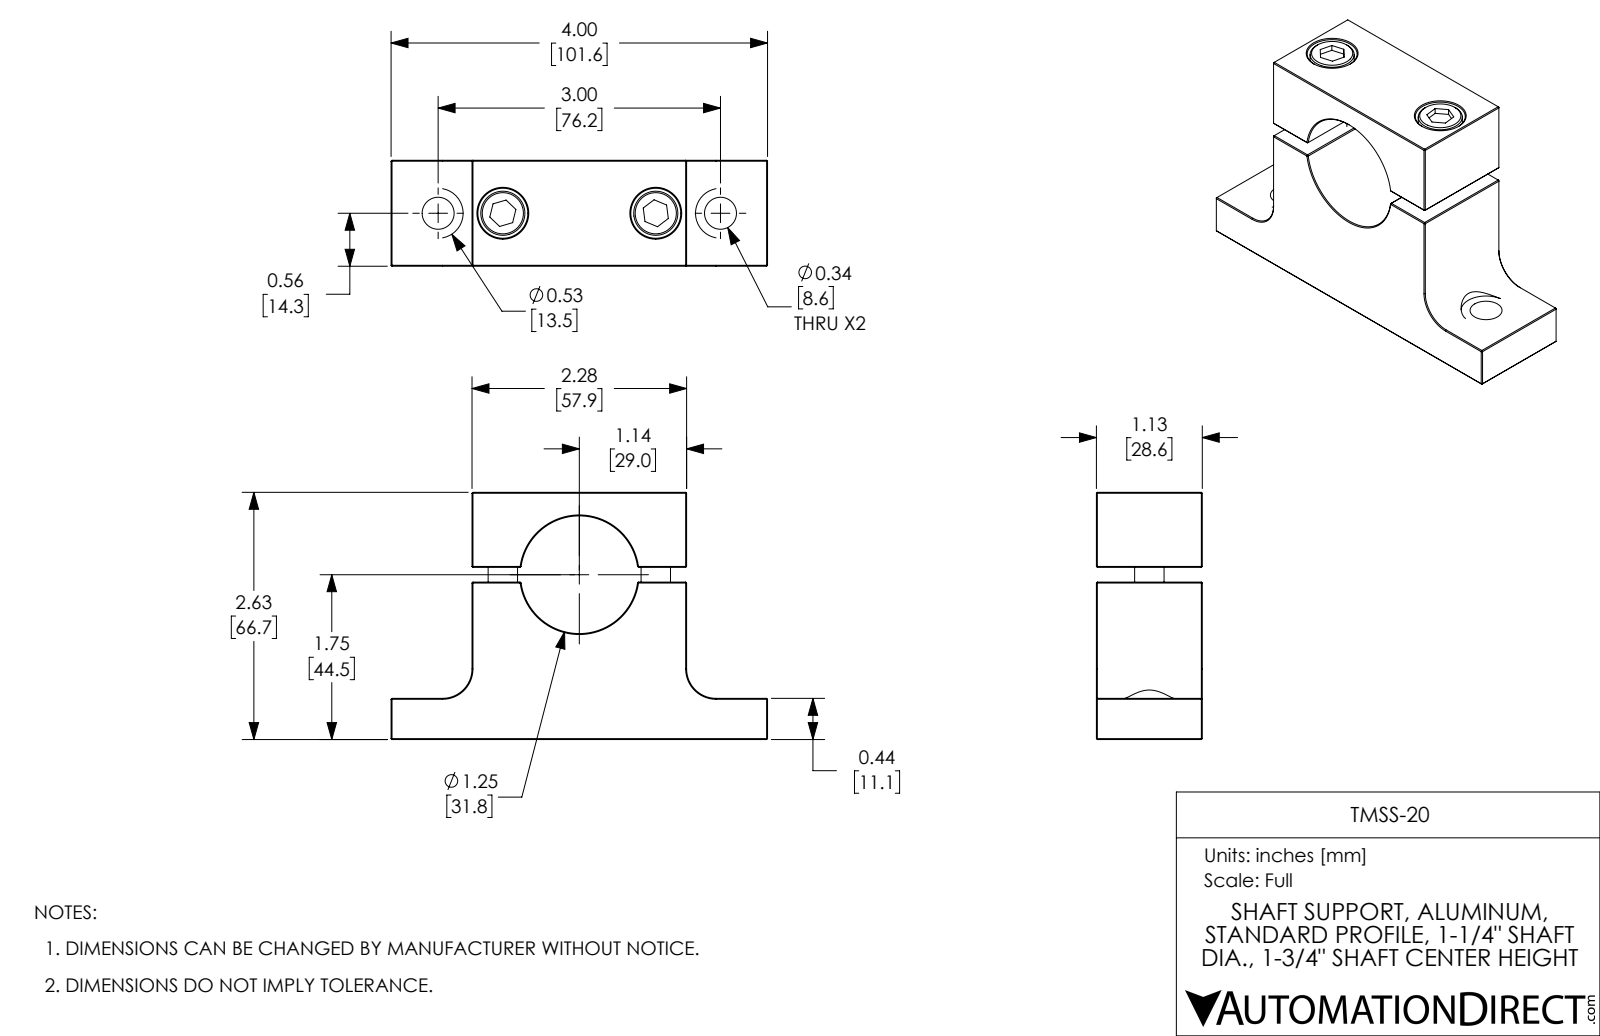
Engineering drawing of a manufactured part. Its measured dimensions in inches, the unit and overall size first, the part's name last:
Units: inches
Overall size (bounding box): 4 × 2.625 × 1.125
Round holes (diameter × count): ⌀0.252 ×2, ⌀0.332 ×2, ⌀0.34 ×2, ⌀0.531 ×2, ⌀1.25 ×1
Round bosses / shafts (diameter × count): ⌀0.469 ×2, ⌀0.313 ×2
Partial cylindrical surfaces — rounded edges, fillets, slot ends (radius × count): R0.266 ×2, R0.313 ×2
Main face-to-face distances: 1.125, 2.625, 2.28, 0.437, 2.187, 1.672, 1.235, 0.953, 1.828, 1.391
Hole centre spacings: 0.687, 2.313, 1.625, 3
Volume: 5.882 in³ · Surface area: 39.99 in²
Bodies: 4 solids, 166 faces (110 planar, 31 cylindrical, 25 other)
Part name (STEP PRODUCT): TMSS-20
STEP written by: SolidWorks 2017 (AUTOMOTIVE_DESIGN)
